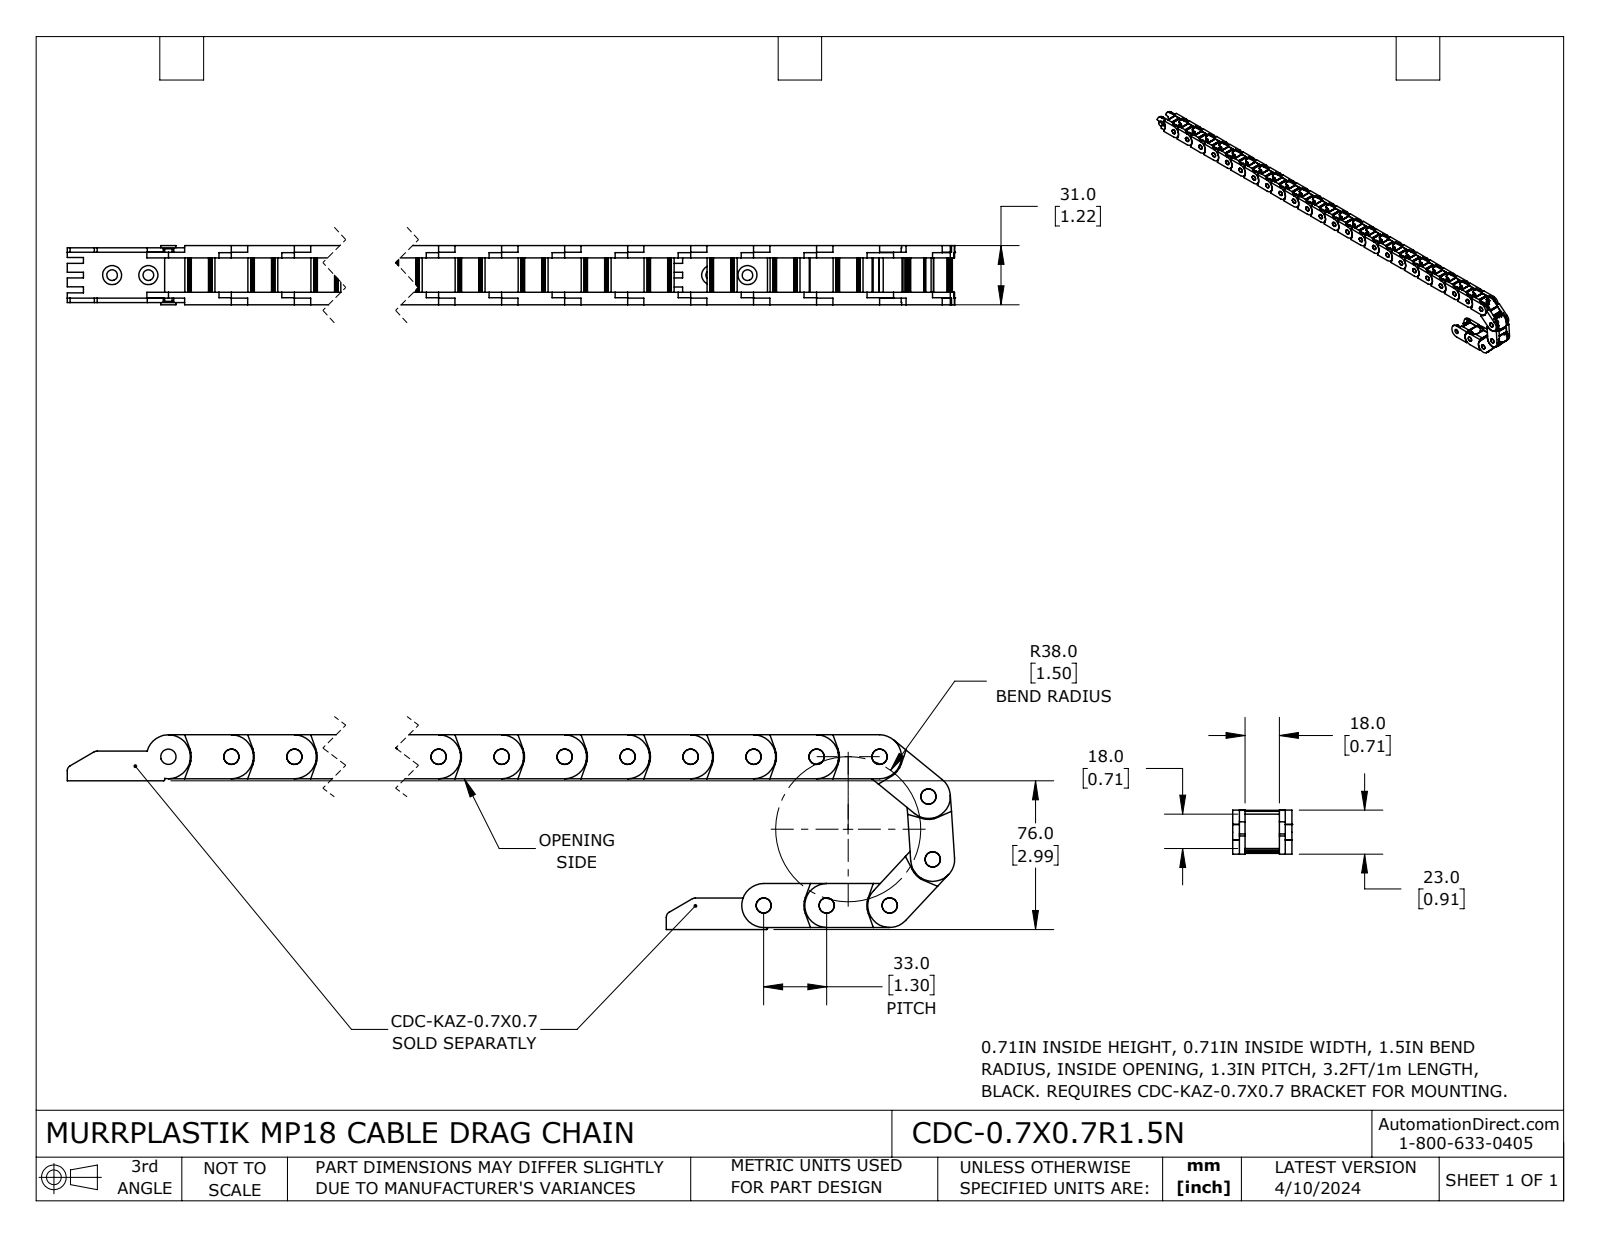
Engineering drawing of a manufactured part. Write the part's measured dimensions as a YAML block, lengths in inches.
part_name: "CDC-0.7X0.7R1.5N"
step_written_by: "SolidWorks 2023 (CONFIG_CONTROL_DESIGN)"
units: inches
bodies: {solids: 29, faces: 2697, planar: 1479, cylindrical: 1218, other: 0}
overall_size: [33.175, 3.972, 1.22]
volume: 17.59
surface_area: 318.3
round_holes:
  - {diameter: 0.315, count: 29}
round_bosses_or_shafts:
  - {diameter: 0.315, count: 1}
partial_cylinders:
  - {radius: 0.02, count: 116}
  - {radius: 0.059, count: 116}
  - {radius: 0.008, count: 58}
  - {radius: 0.012, count: 58}
  - {radius: 0.453, count: 30}
  - {radius: 0.47, count: 30}
  - {radius: 0.197, count: 29}
  - {radius: 0.215, count: 29}
face_to_face_distances: [0.256, 0.965, 1.22, 0.709, 0.138, 1.083, 0.118, 0.827, 0.146, 1.075]
hole_center_spacings: [1.299, 2.598, 3.898, 5.197, 6.496, 7.795, 9.094, 10.394]
